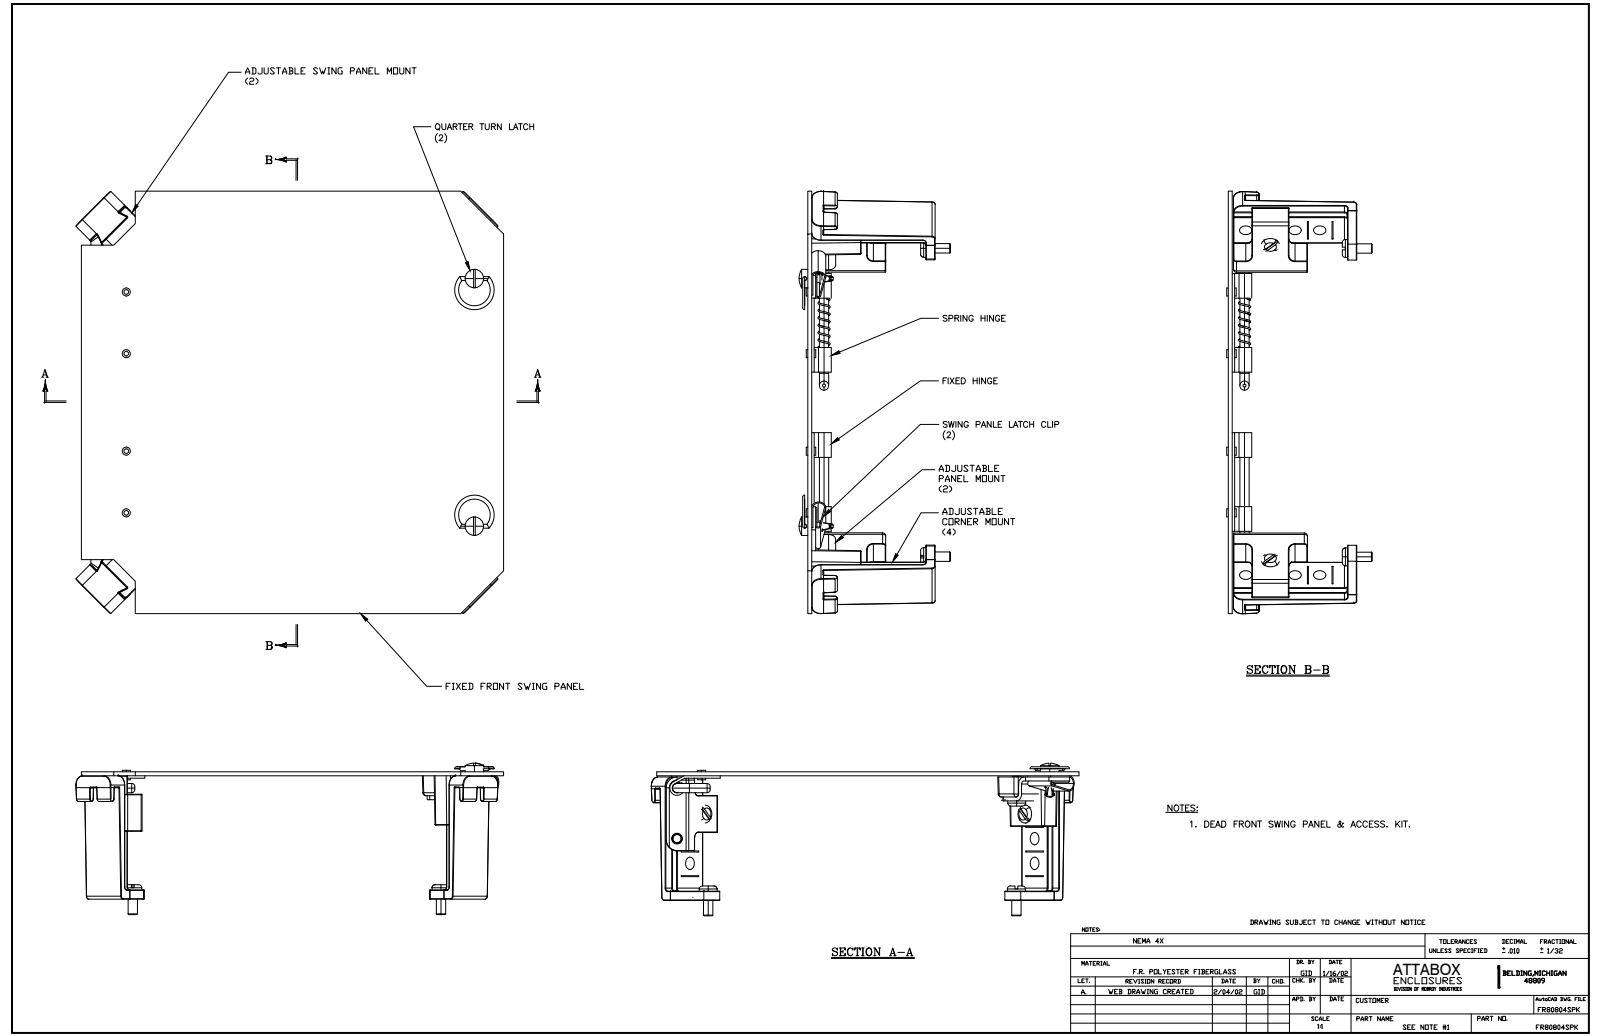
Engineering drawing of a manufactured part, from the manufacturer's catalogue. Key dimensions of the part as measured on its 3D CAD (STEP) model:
Part name (STEP PRODUCT): FR80804SPK
STEP written by: SolidWorks 2019 (AUTOMOTIVE_DESIGN)
Units: inches
Bodies: 44 solids, 1433 faces (586 planar, 453 cylindrical, 394 other)
Overall size (bounding box): 8.563 × 8.563 × 3.178
Volume: 12.13 in³ · Surface area: 246.5 in²
Round holes (diameter × count): ⌀0.25 ×20, ⌀0.253 ×6, ⌀0.05 ×4, ⌀0.14 ×4, ⌀0.144 ×4, ⌀0.217 ×4, ⌀0.22 ×4, ⌀0.156 ×2, ⌀0.197 ×2, ⌀0.312 ×2, ⌀0.35 ×2, ⌀0.079 ×1
Round bosses / shafts (diameter × count): ⌀0.19 ×10, ⌀0.373 ×6, ⌀0.433 ×4, ⌀0.315 ×4, ⌀0.16 ×4, ⌀0.079 ×4, ⌀0.394 ×2, ⌀0.362 ×2
Partial cylindrical surfaces — rounded edges, fillets, slot ends (radius × count): R0.01 ×218, R0.06 ×40, R0.063 ×10, R0.025 ×8, R0.062 ×8, R0.13 ×8, R0.049 ×4, R0.19 ×4
Main face-to-face distances: 0.08, 0.079, 9.881, 0.159, 0.164, 0.084, 0.08, 2.666, 2.586, 2.507
Hole centre spacings: 0.5, 1, 1.5, 0.837, 0.872, 6.25, 6.252, 6.25
